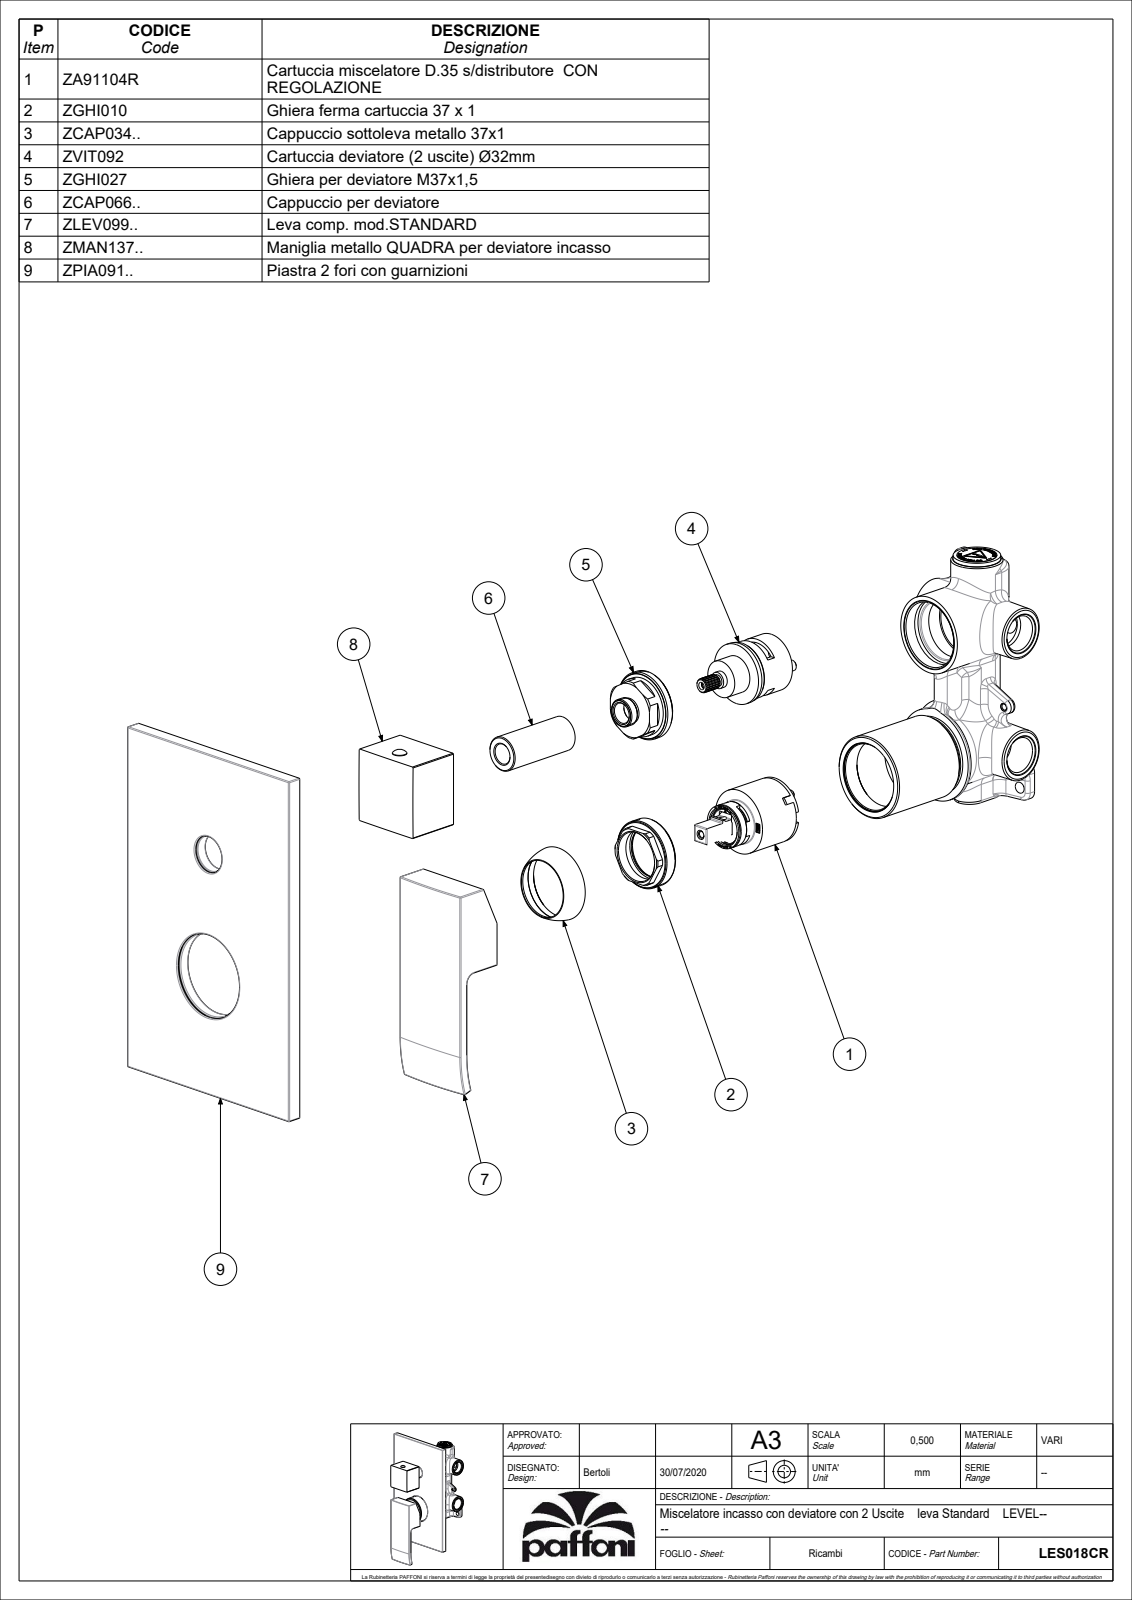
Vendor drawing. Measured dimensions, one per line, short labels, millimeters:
name: LES018CR
written by: CREO PARAMETRIC BY PTC INC, 2020044 (CONFIG_CONTROL_DESIGN)
unit: mm
bodies: 4 solids, 1086 faces (605 planar, 286 cylindrical, 195 other)
size: 213.07 × 120 × 56.39
volume: 217 004 mm³; area: 114 804 mm²
holes: 2× ⌀3, 2× ⌀4, 2× ⌀5.5, 2× ⌀36, 1× ⌀3.2, 1× ⌀4.2, 1× ⌀4.5, 1× ⌀5, 1× ⌀7.8, 1× ⌀11, 1× ⌀14.8, 1× ⌀19.2
bosses: 2× ⌀7.6, 1× ⌀51, 1× ⌀49, 1× ⌀44.8, 1× ⌀35, 1× ⌀25, 1× ⌀23.5, 1× ⌀23.4
rounds: 20× R0.5, 14× R1.5, 11× R0.15, 10× R1, 4× R0.3, 4× R2, 2× R300, 1× R2.25
face distances: 8, 2.5, 5.5, 40, 37.5, 82.5, 42.5, 17.5, 80, 22.5
hole spacings: 6.8, 8, 10, 14.8, 58, 68
